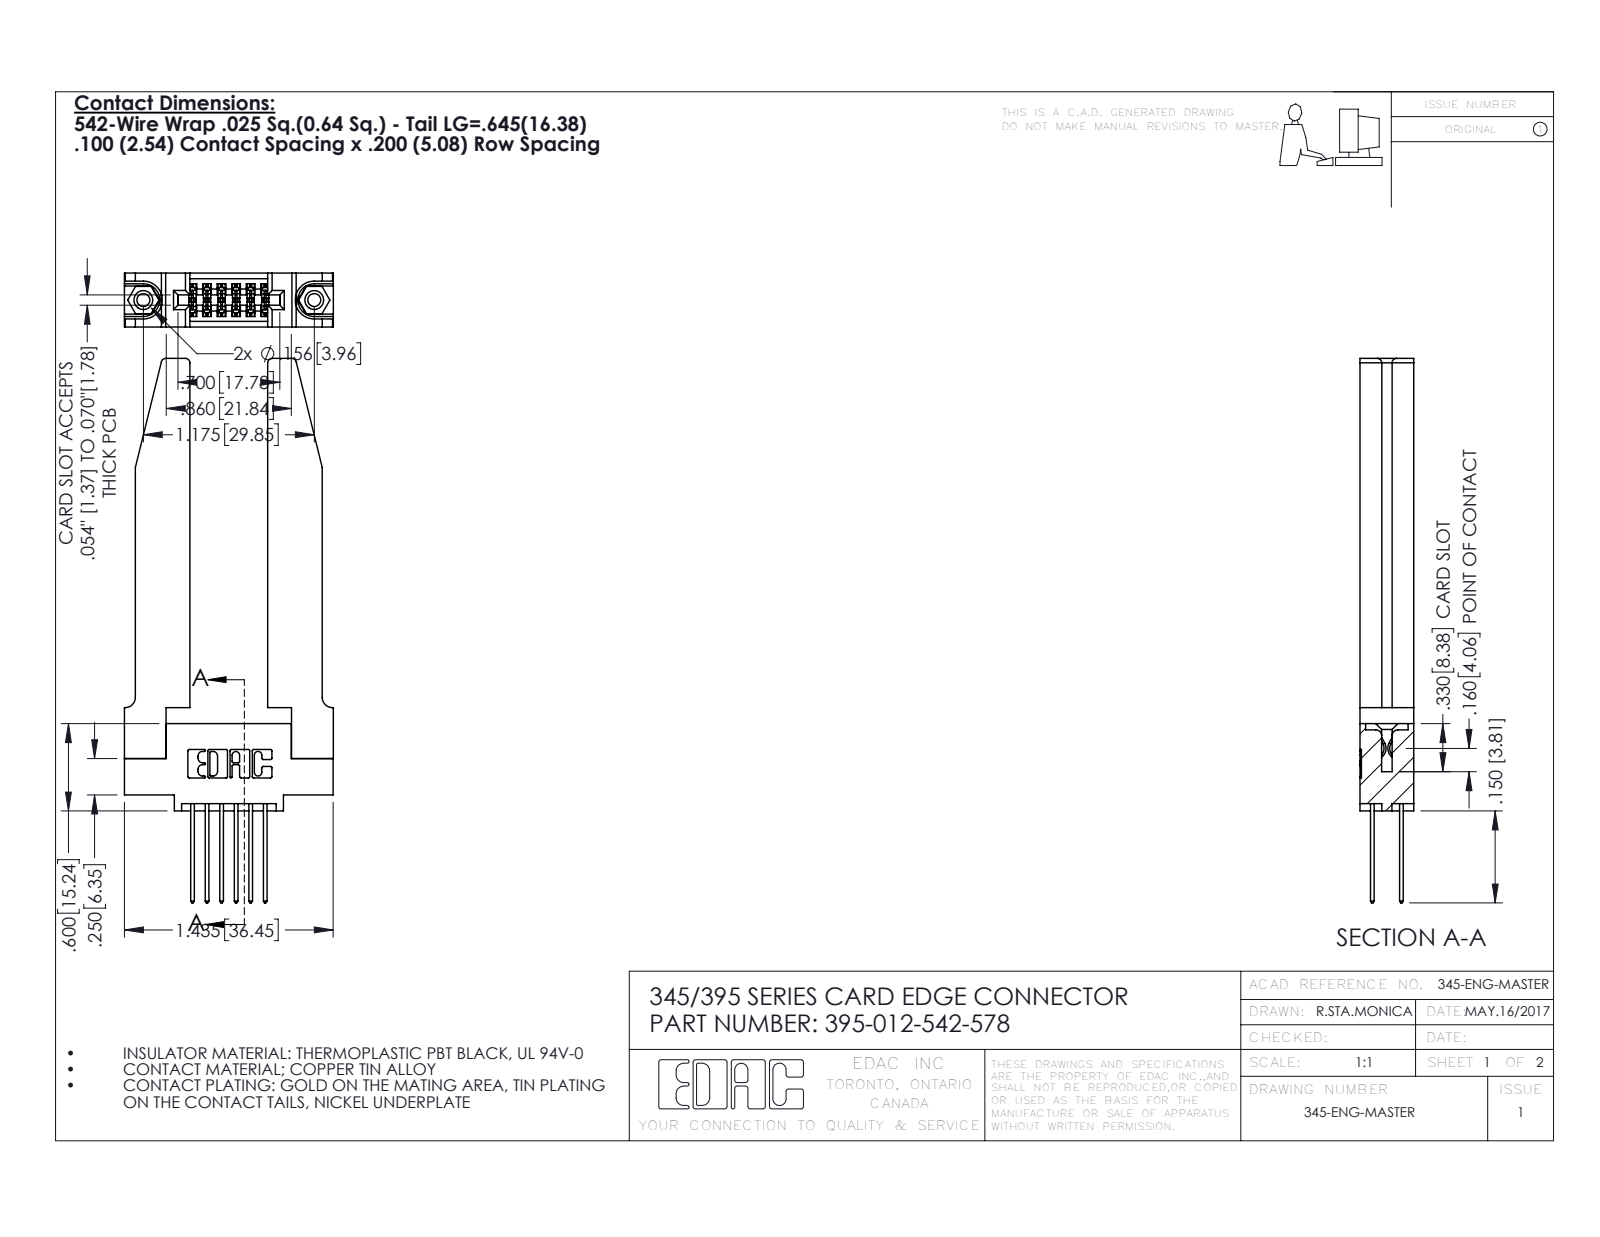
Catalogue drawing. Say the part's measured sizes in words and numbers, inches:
The part is named "345-292-001_345-293-142; 395-012-542-578; 345 Part_0.110 Offset - 0.156 Dia-TH; 345-220-078_345-220-078 (+1 more)". Its 3-D file was written by "SolidWorks 2016 (CONFIG_CONTROL_DESIGN)". It is 17 solids with 964 faces: 622 planar, 290 cylindrical and 52 other. Overall it measures 3.742 by 1.436 by 0.37 inches. Its volume is 0.669 cubic inches and its surface area 17.38 square inches. Round holes: 2 of diameter 0.089, 2 of diameter 0.125, 2 of diameter 0.156, 1 of diameter 0.064. Round bosses or shafts: 2 of diameter 0.155. Partial cylindrical surfaces (rounded edges, fillets, slot ends): 22 of radius 0.01, 18 of radius 0.006, 12 of radius 0.01, 8 of radius 0.03, 6 of radius 0.007, 6 of radius 0.031, 3 of radius 0.026, 2 of radius 0.014. The main face-to-face distances are 0.37, 0.072, 0.298, 0.148, 0.15, 0.22, 0.077, 0.535, 0.2, 0.098. The hole center spacings are 0.27, 0.946, 1.175.
